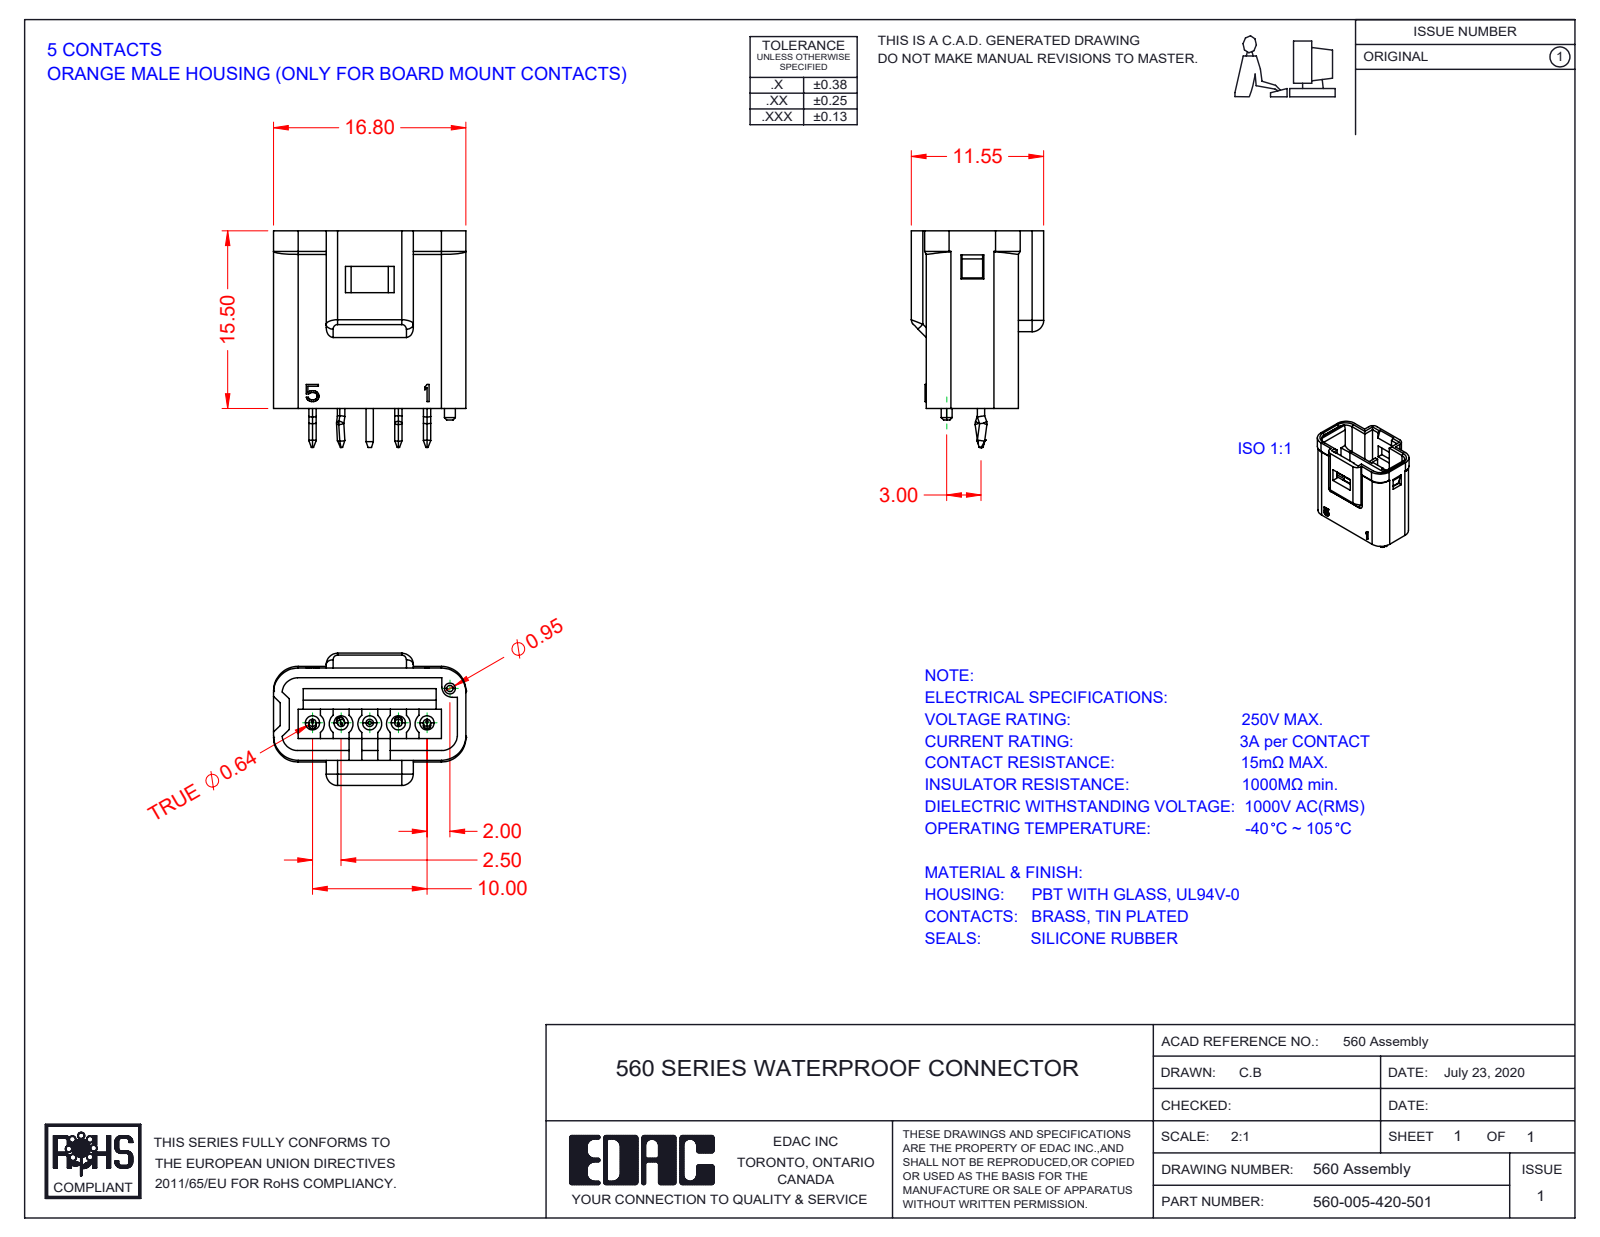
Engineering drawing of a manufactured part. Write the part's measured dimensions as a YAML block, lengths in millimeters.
part_name: "PCB-HEADER-CONTACT-5P; FACIAL_SEAL_5POS; PCB-HEADER-HOUSING-5P_ORANGE; CONTACT_PCB-HEADER-2 (+5 more)"
step_written_by: "SolidWorks 2020 (CONFIG_CONTROL_DESIGN)"
units: millimeters
bodies: {solids: 8, faces: 772, planar: 448, cylindrical: 184, other: 140}
overall_size: [18.9, 16.8, 11.55]
volume: 1028
surface_area: 2869
round_holes:
  - {diameter: 0.64, count: 5}
  - {diameter: 1.4, count: 5}
  - {diameter: 1.1, count: 1}
round_bosses_or_shafts:
  - {diameter: 0.64, count: 8}
  - {diameter: 0.95, count: 1}
partial_cylinders:
  - {radius: 1, count: 25}
  - {radius: 0.25, count: 16}
  - {radius: 0.35, count: 12}
  - {radius: 1.65, count: 8}
  - {radius: 2.15, count: 8}
  - {radius: 0.3, count: 4}
  - {radius: 0.5, count: 4}
  - {radius: 1.1, count: 4}
face_to_face_distances: [0.6, 7.45, 3.6, 8.05, 1.1, 7.4, 6.8, 1.9, 6.85, 2.5]
hole_center_spacings: [2.5, 5, 3.14, 5.35, 7.5, 1.9, 10]
